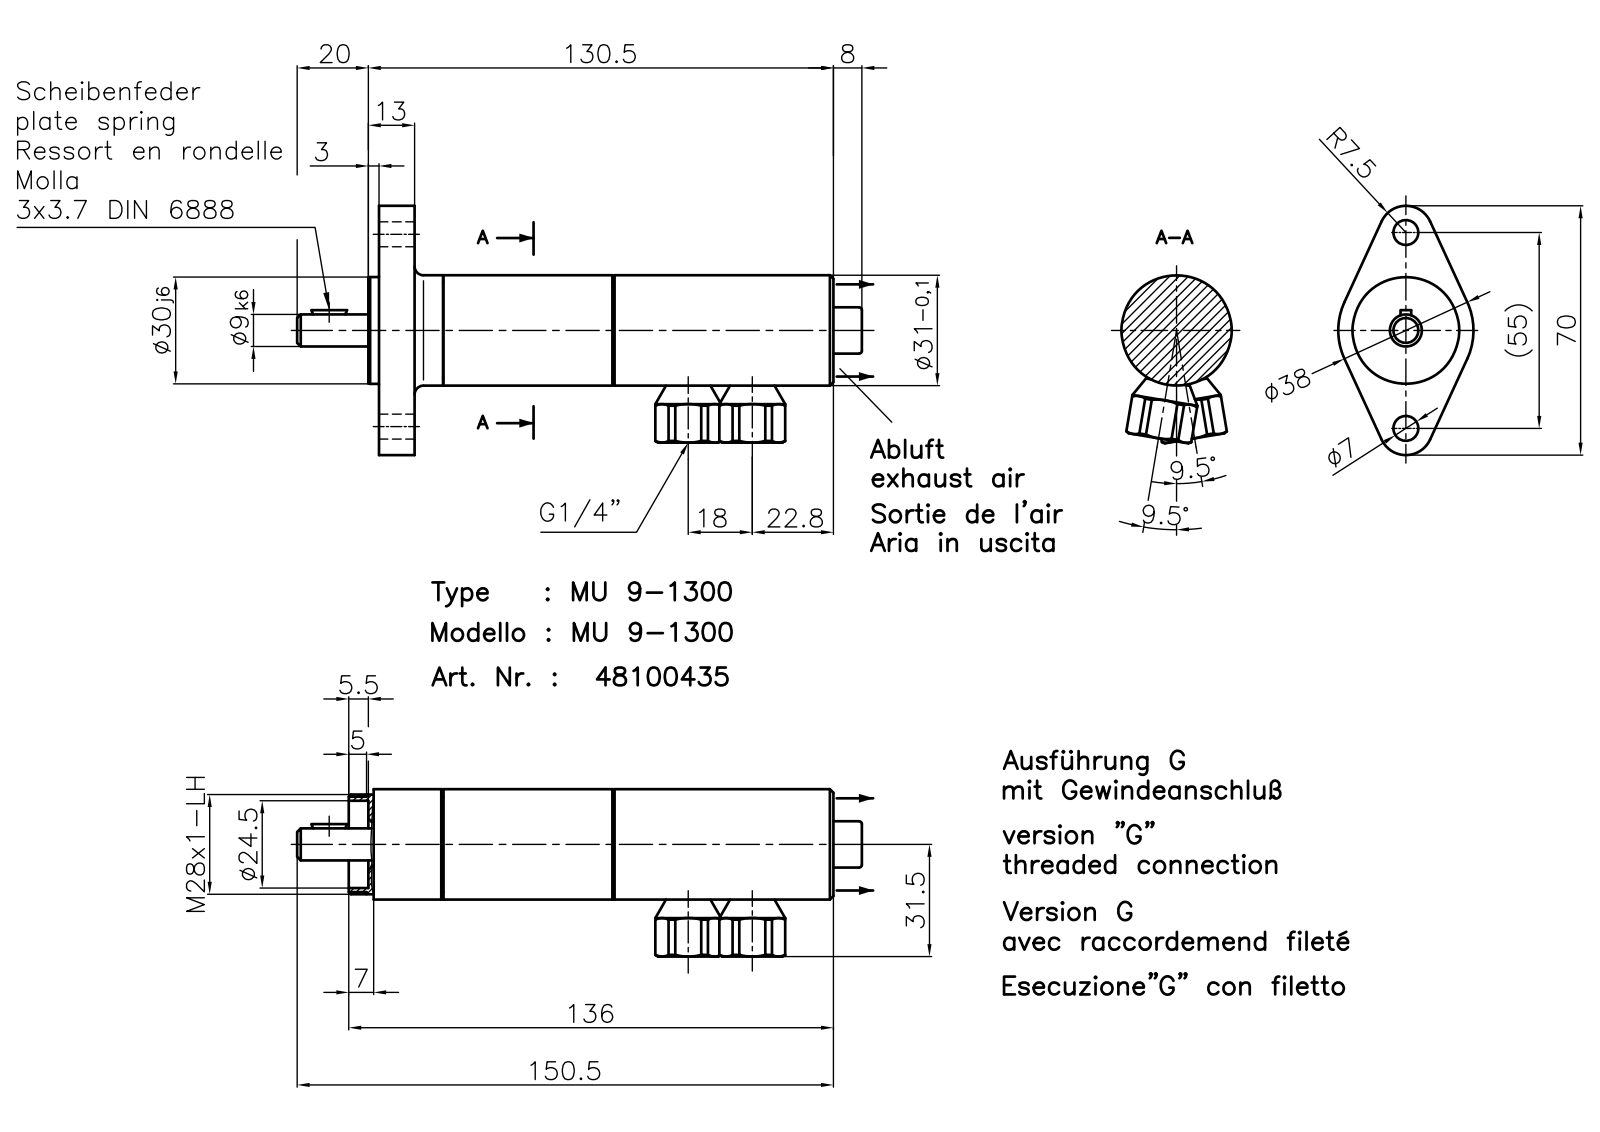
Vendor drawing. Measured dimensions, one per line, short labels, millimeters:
name: MU 9-1300_48100437
written by: Autodesk Inventor 2008 (AUTOMOTIVE_DESIGN)
unit: mm
bodies: 1 solid, 137 faces (59 planar, 48 cylindrical, 30 other)
size: 158.6 × 70 × 38
volume: 113 228 mm³; area: 25 186 mm²
holes: 2× ⌀6.5, 2× ⌀7, 1× ⌀2.8, 1× ⌀9.5, 1× ⌀10, 1× ⌀27, 1× ⌀28, 1× ⌀29.3
bosses: 1× ⌀31, 1× ⌀30, 1× ⌀26.78, 1× ⌀26.66, 1× ⌀13, 1× ⌀9, 1× ⌀8
rounds: 2× R7, 2× R7.5, 2× R9.25, 1× R5, 1× R5.25, 1× R19
face distances: 10, 3, 117.7, 13, 127.7, 130.7, 37.98, 17, 1.1, 8
hole spacings: 27.5, 55
